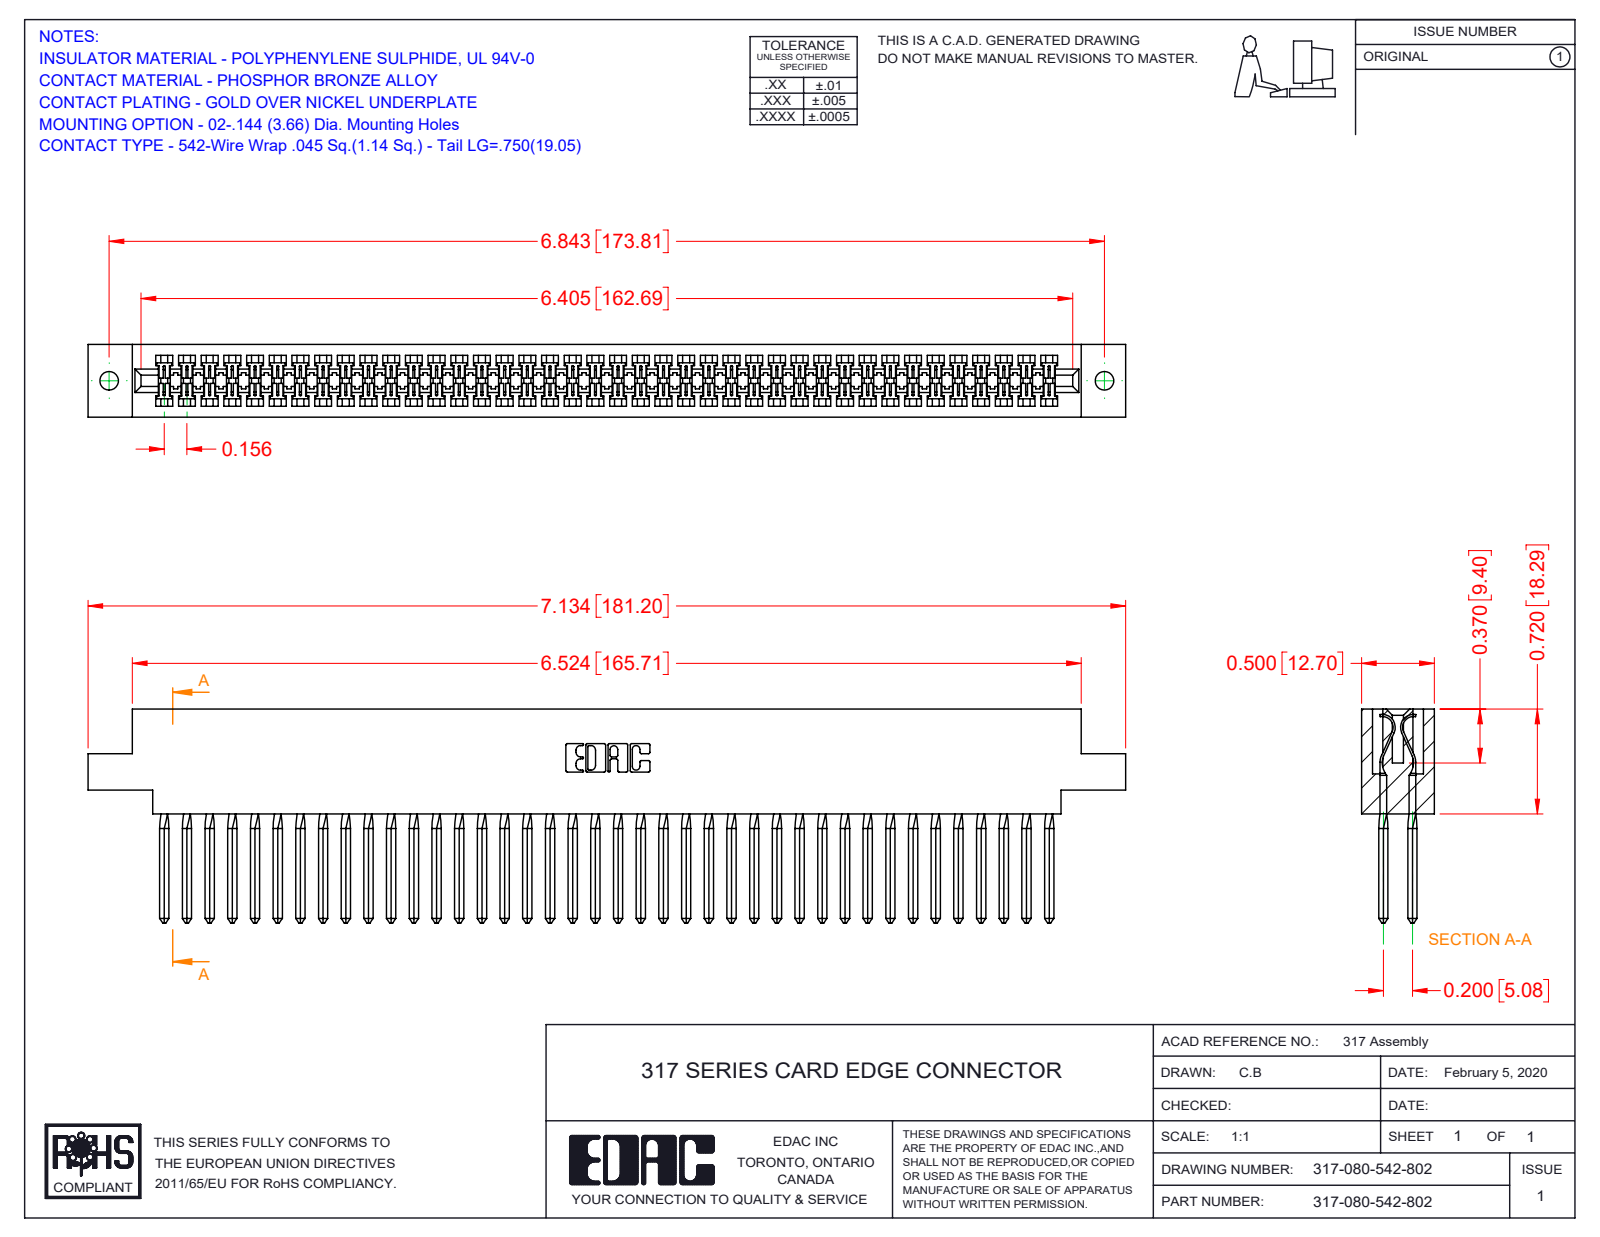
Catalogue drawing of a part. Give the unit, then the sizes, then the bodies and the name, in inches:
Units: inches
Overall size (bounding box): 7.134 × 1.47 × 0.5
Round holes (diameter × count): ⌀0.128 ×2
Partial cylindrical surfaces — rounded edges, fillets, slot ends (radius × count): R0.006 ×160, R0.01 ×22, R0.007 ×6, R0.031 ×6, R0.026 ×3, R0.074 ×2, R0.089 ×2, R0.1 ×2
Main face-to-face distances: 0.5, 0.075, 0.425, 0.35, 0.2, 0.046, 0.128, 0.372, 0.052, 0.297
Hole centre spacings: 6.843
Volume: 1.805 in³ · Surface area: 63.23 in²
Bodies: 81 solids, 4662 faces (3738 planar, 604 cylindrical, 320 other)
Part name (STEP PRODUCT): 317-080-542-802; 317 Part_.144 Dia; 317-290-003_542
STEP written by: SolidWorks 2016 (CONFIG_CONTROL_DESIGN)
